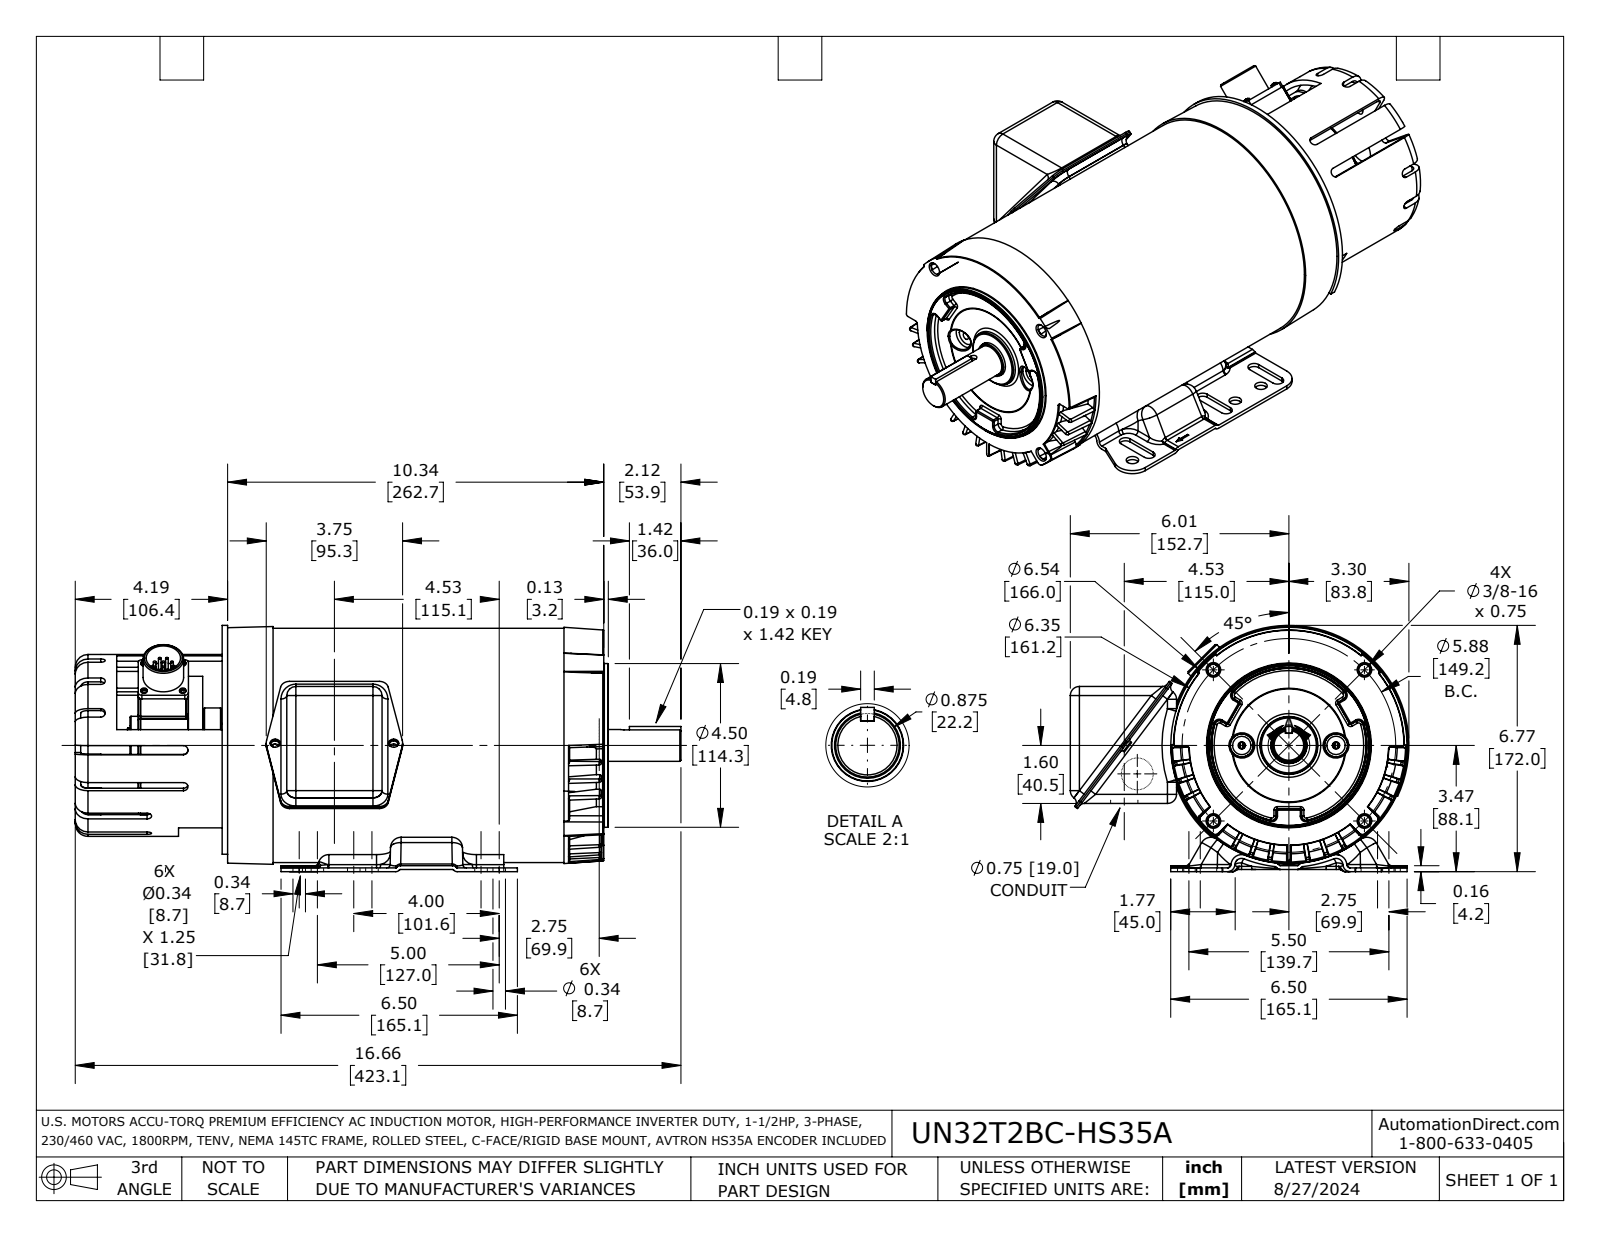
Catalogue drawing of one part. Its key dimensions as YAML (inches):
part_name: "UN32T2BC-HS35A"
step_written_by: "SolidWorks 2021 (AUTOMOTIVE_DESIGN)"
units: inches
bodies: {solids: 26, faces: 3056, planar: 755, cylindrical: 719, other: 1582}
overall_size: [16.656, 9.311, 6.77]
volume: 103.1
surface_area: 1168
round_holes:
  - {diameter: 0.25, count: 8}
  - {diameter: 0.344, count: 6}
  - {diameter: 0.4, count: 6}
  - {diameter: 0.12, count: 4}
  - {diameter: 0.2, count: 4}
  - {diameter: 0.302, count: 4}
  - {diameter: 0.421, count: 4}
  - {diameter: 0.55, count: 4}
  - {diameter: 0.136, count: 3}
  - {diameter: 0.098, count: 2}
  - {diameter: 0.173, count: 2}
  - {diameter: 0.229, count: 2}
round_bosses_or_shafts:
  - {diameter: 0.072, count: 8}
  - {diameter: 0.175, count: 4}
  - {diameter: 0.12, count: 4}
  - {diameter: 0.15, count: 3}
  - {diameter: 0.325, count: 2}
  - {diameter: 0.072, count: 2}
  - {diameter: 6.44, count: 1}
  - {diameter: 6.315, count: 1}
partial_cylinders:
  - {radius: 0.062, count: 91}
  - {radius: 0.031, count: 71}
  - {radius: 0.125, count: 42}
  - {radius: 0.25, count: 26}
  - {radius: 0.202, count: 18}
  - {radius: 0.094, count: 14}
  - {radius: 0.048, count: 12}
  - {radius: 0.172, count: 12}
face_to_face_distances: [0.048, 1.08, 1.375, 2.455, 0.15, 4.04, 0.104, 0.12, 0.53, 0.06]
hole_center_spacings: [2.098, 2.246, 3.419, 4.349, 5.422, 2.073, 2.232, 2.234]
